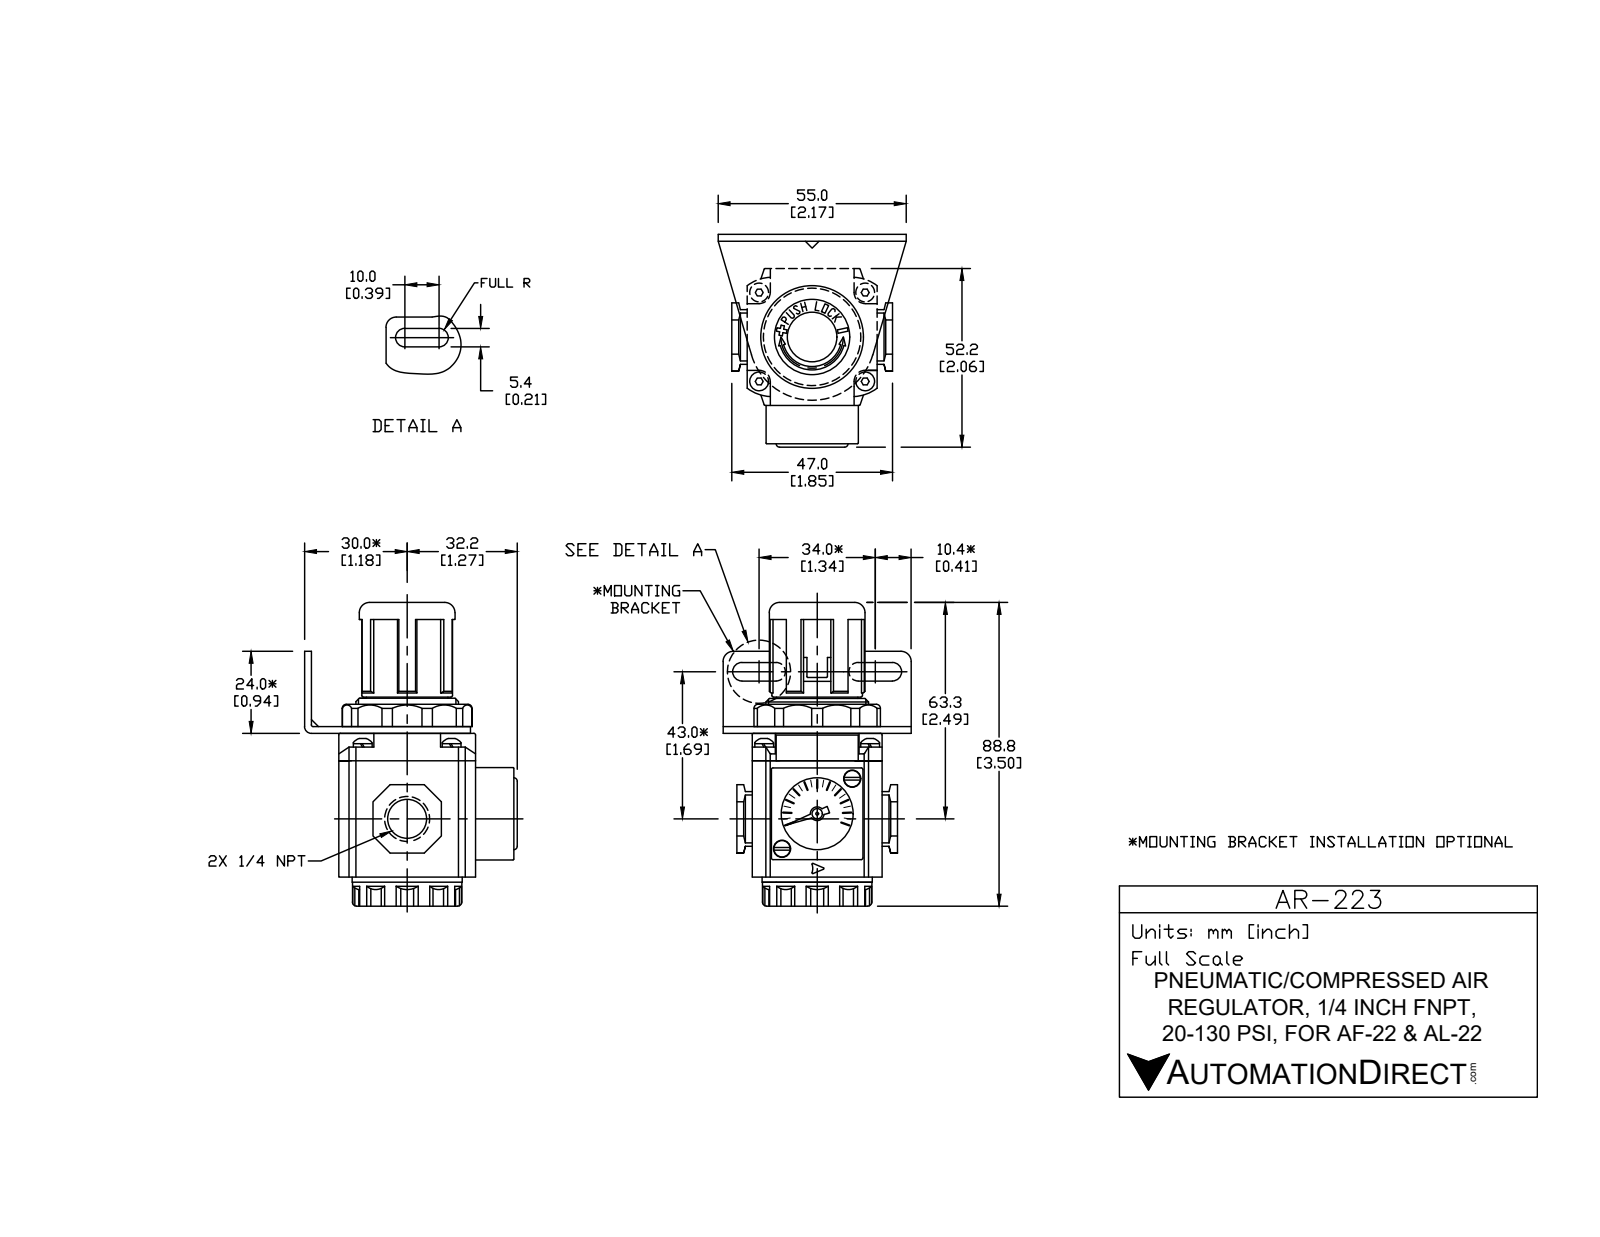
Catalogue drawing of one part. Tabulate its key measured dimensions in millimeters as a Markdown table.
| quantity | value |
| --- | --- |
| part name | AR-223 |
| STEP written by | SolidWorks 2015 (CONFIG_CONTROL_DESIGN) |
| units | millimeters |
| bodies | 14 solids, 491 faces (326 planar, 133 cylindrical, 32 other) |
| overall size | 88.8 × 62 × 55 |
| volume | 100 911 mm³ |
| surface area | 29 790 mm² |
| round holes (diameter × count) | 3 × 6, 2 × 1, 11.13 × 1, 21 × 1, 22 × 1, 30 × 1 |
| round bosses / shafts (diameter × count) | 5.5 × 4, 2.7 × 2, 32 × 1, 31.36 × 1, 28 × 1, 23.8 × 1, 14 × 1, 4 × 1 |
| partial cylindrical surfaces (radius × count) | 1.2 × 10, 1 × 8, 3.25 × 6, 0.3 × 4, 2.75 × 4, 12 × 4, 0.2 × 3, 2 × 1 |
| main face-to-face distances | 2, 42, 10, 44, 39, 40, 38, 50, 1, 11 |
| hole center spacings | 20.23, 14.5, 26, 31, 40.46, 28.99 |
